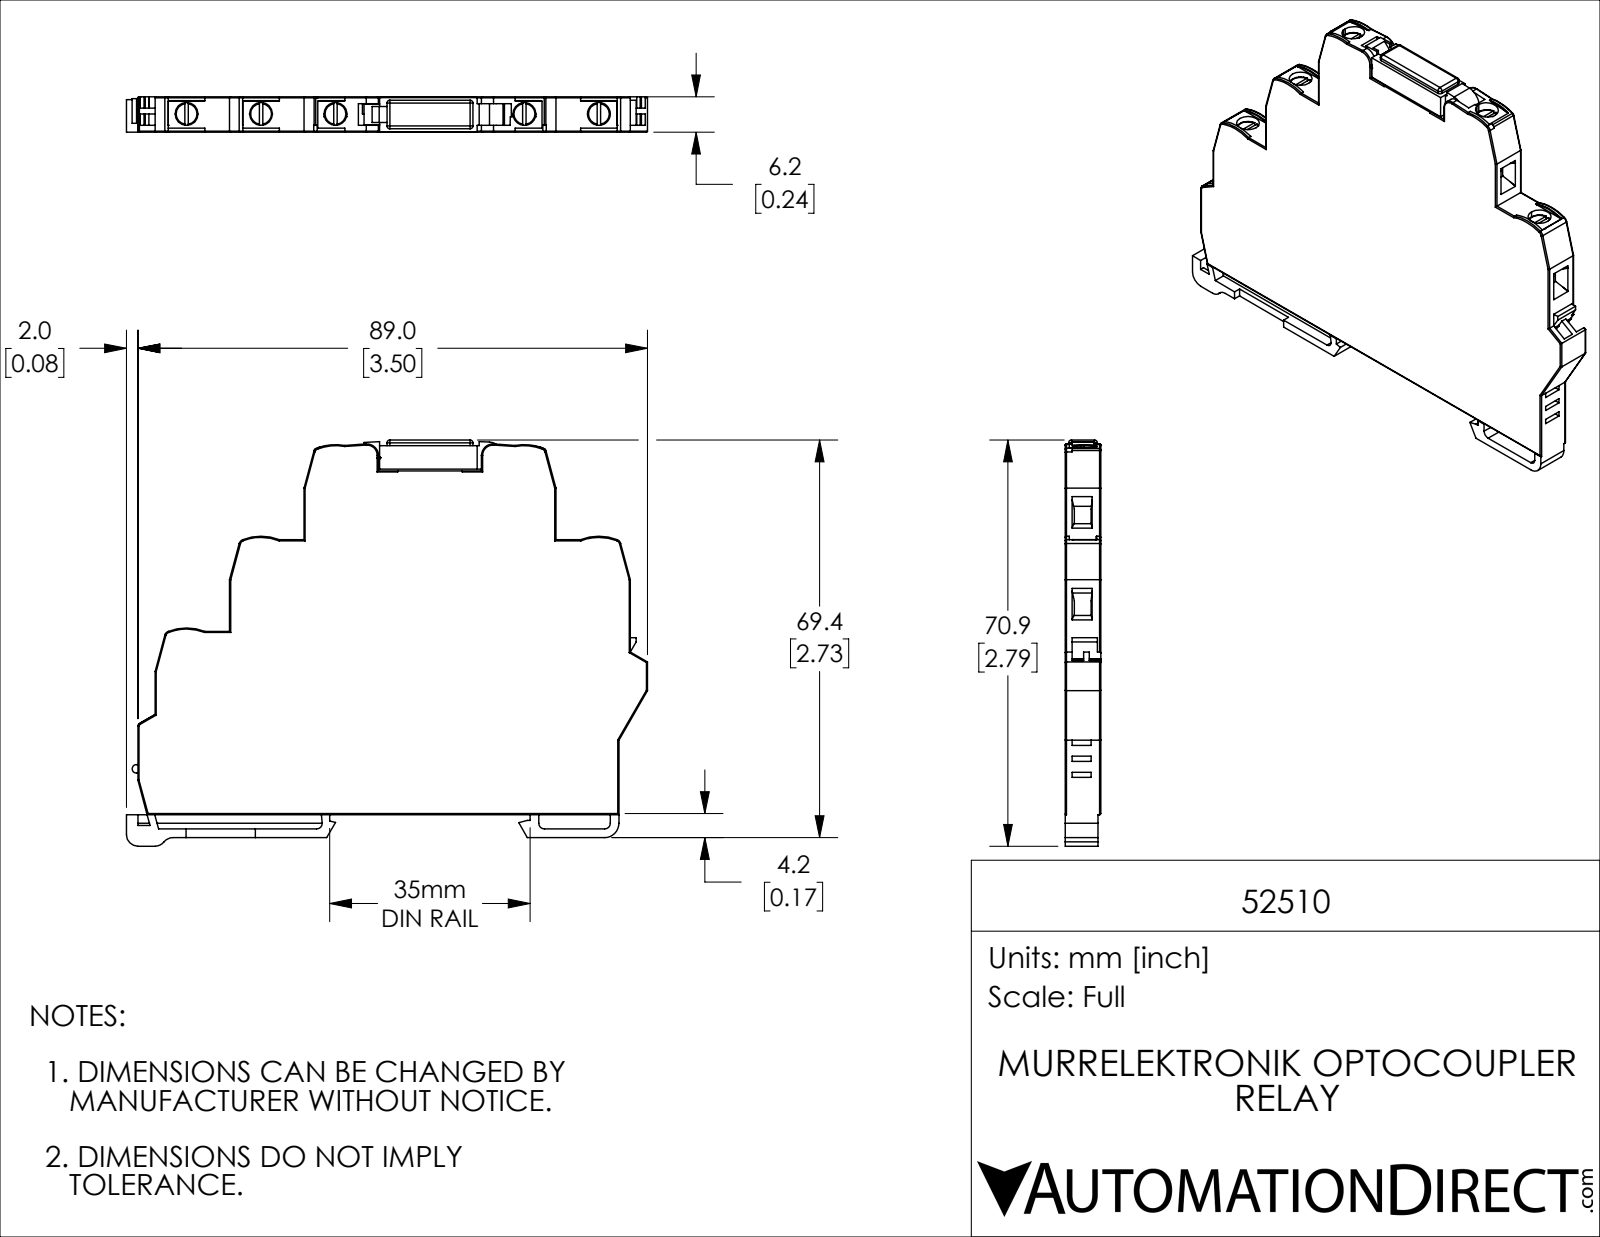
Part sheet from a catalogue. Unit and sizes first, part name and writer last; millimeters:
Units: millimetres
Overall size (bounding box): 91 × 70.9 × 6.2
Round holes (diameter × count): ⌀4 ×5, ⌀1.9 ×1
Round bosses / shafts (diameter × count): ⌀2 ×1
Partial cylindrical surfaces — rounded edges, fillets, slot ends (radius × count): R0.2 ×56, R0.5 ×11, R1 ×8, R2 ×6, R0.8 ×5, R8.8 ×5, R0.1 ×4, R0.4 ×3
Main face-to-face distances: 6.2, 1.5, 5, 2.5, 4, 3, 1.2, 0.5, 1, 60
Hole centre spacings: 13, 46, 59, 26, 33, 72
Volume: 27 960 mm³ · Surface area: 12 990 mm²
Bodies: 2 solids, 566 faces (351 planar, 147 cylindrical, 68 other)
Part name (STEP PRODUCT): 52510
STEP written by: SolidWorks 2019 (CONFIG_CONTROL_DESIGN)
